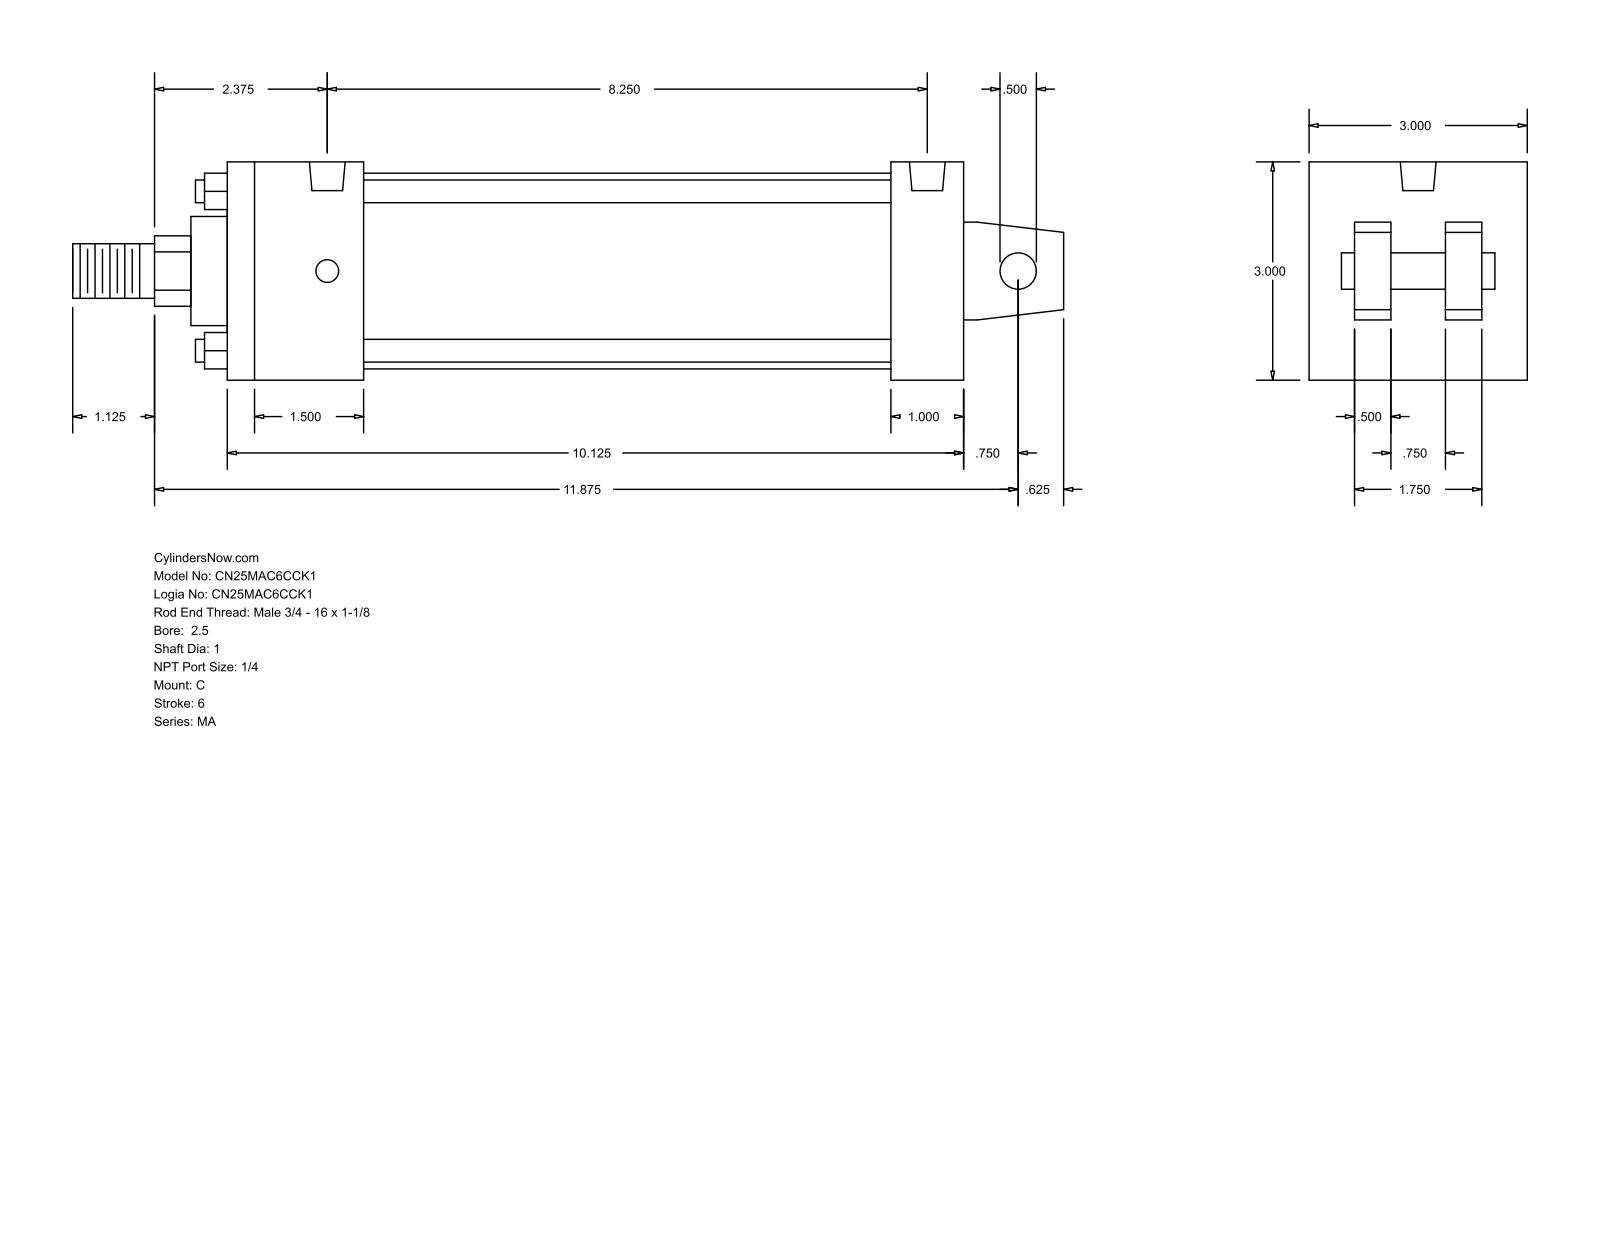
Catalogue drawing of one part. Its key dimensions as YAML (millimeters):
part_name: "MA_C__0250_1"
step_written_by: "GSSL Pune (CONFIG_CONTROL_DESIGN)"
units: millimeters
bodies: {solids: 0, faces: 103, planar: 76, cylindrical: 27, other: 0}
overall_size: [346.07, 76.2, 76.2]
round_holes:
  - {diameter: 7.94, count: 4}
  - {diameter: 12.49, count: 2}
round_bosses_or_shafts:
  - {diameter: 7.94, count: 4}
  - {diameter: 68.33, count: 1}
  - {diameter: 38.1, count: 1}
  - {diameter: 25.4, count: 1}
  - {diameter: 19.05, count: 1}
  - {diameter: 12.7, count: 1}
partial_cylinders:
  - {radius: 12.29, count: 1}
face_to_face_distances: [76.2, 47.63, 257.17, 12.7, 60.33, 15.87, 28.57, 231.78, 184.15, 209.54]
hole_center_spacings: [209.55]
